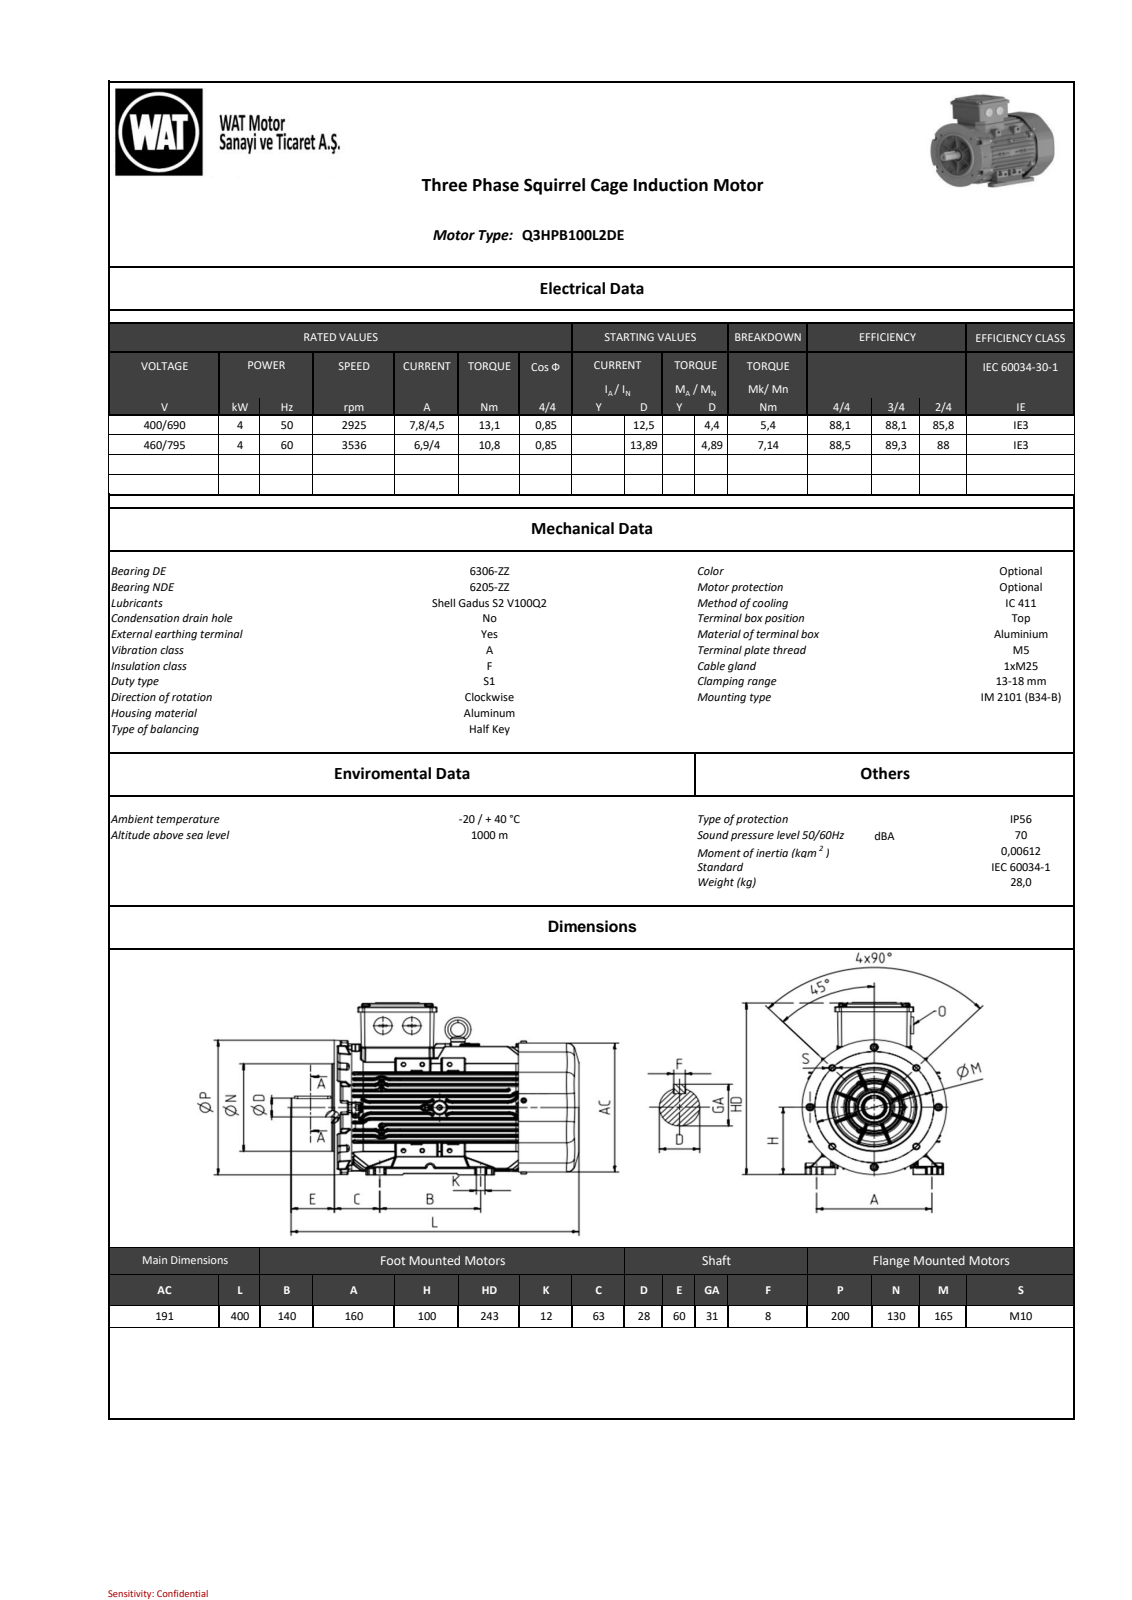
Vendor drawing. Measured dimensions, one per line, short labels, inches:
name: QH series_ 100_B34b_stp_objects
written by: SIEMENS PLM Software NX2206.8101 (AUTOMOTIVE_DESIGN)
unit: in
bodies: 0 solids, 6187 faces (1358 planar, 2473 cylindrical, 2356 other)
size: 15.721 × 10.068 × 7.874
holes: 4× ⌀0.256, 4× ⌀0.335, 1× ⌀0.394, 1× ⌀1.749, 1× ⌀2.26, 1× ⌀3.504, 1× ⌀4.291, 1× ⌀5.079, 1× ⌀5.236
bosses: 8× ⌀0.315, 4× ⌀0.472, 4× ⌀0.236, 4× ⌀0.197, 3× ⌀0.984, 1× ⌀5.118, 1× ⌀4.469, 1× ⌀3.681
rounds: 633× R0.031, 602× R0.039, 113× R0.079, 83× R0.059, 53× R0.02, 52× R0.032, 40× R0.197, 26× R0.591
face distances: 0.336, 0.333, 0.333, 3.002, 0.666, 3.679, 1.007, 0.671, 3.019, 2.348
hole spacings: 3.248, 4.594, 2.52, 2.623, 4.111, 5.039, 5.634, 6.496
